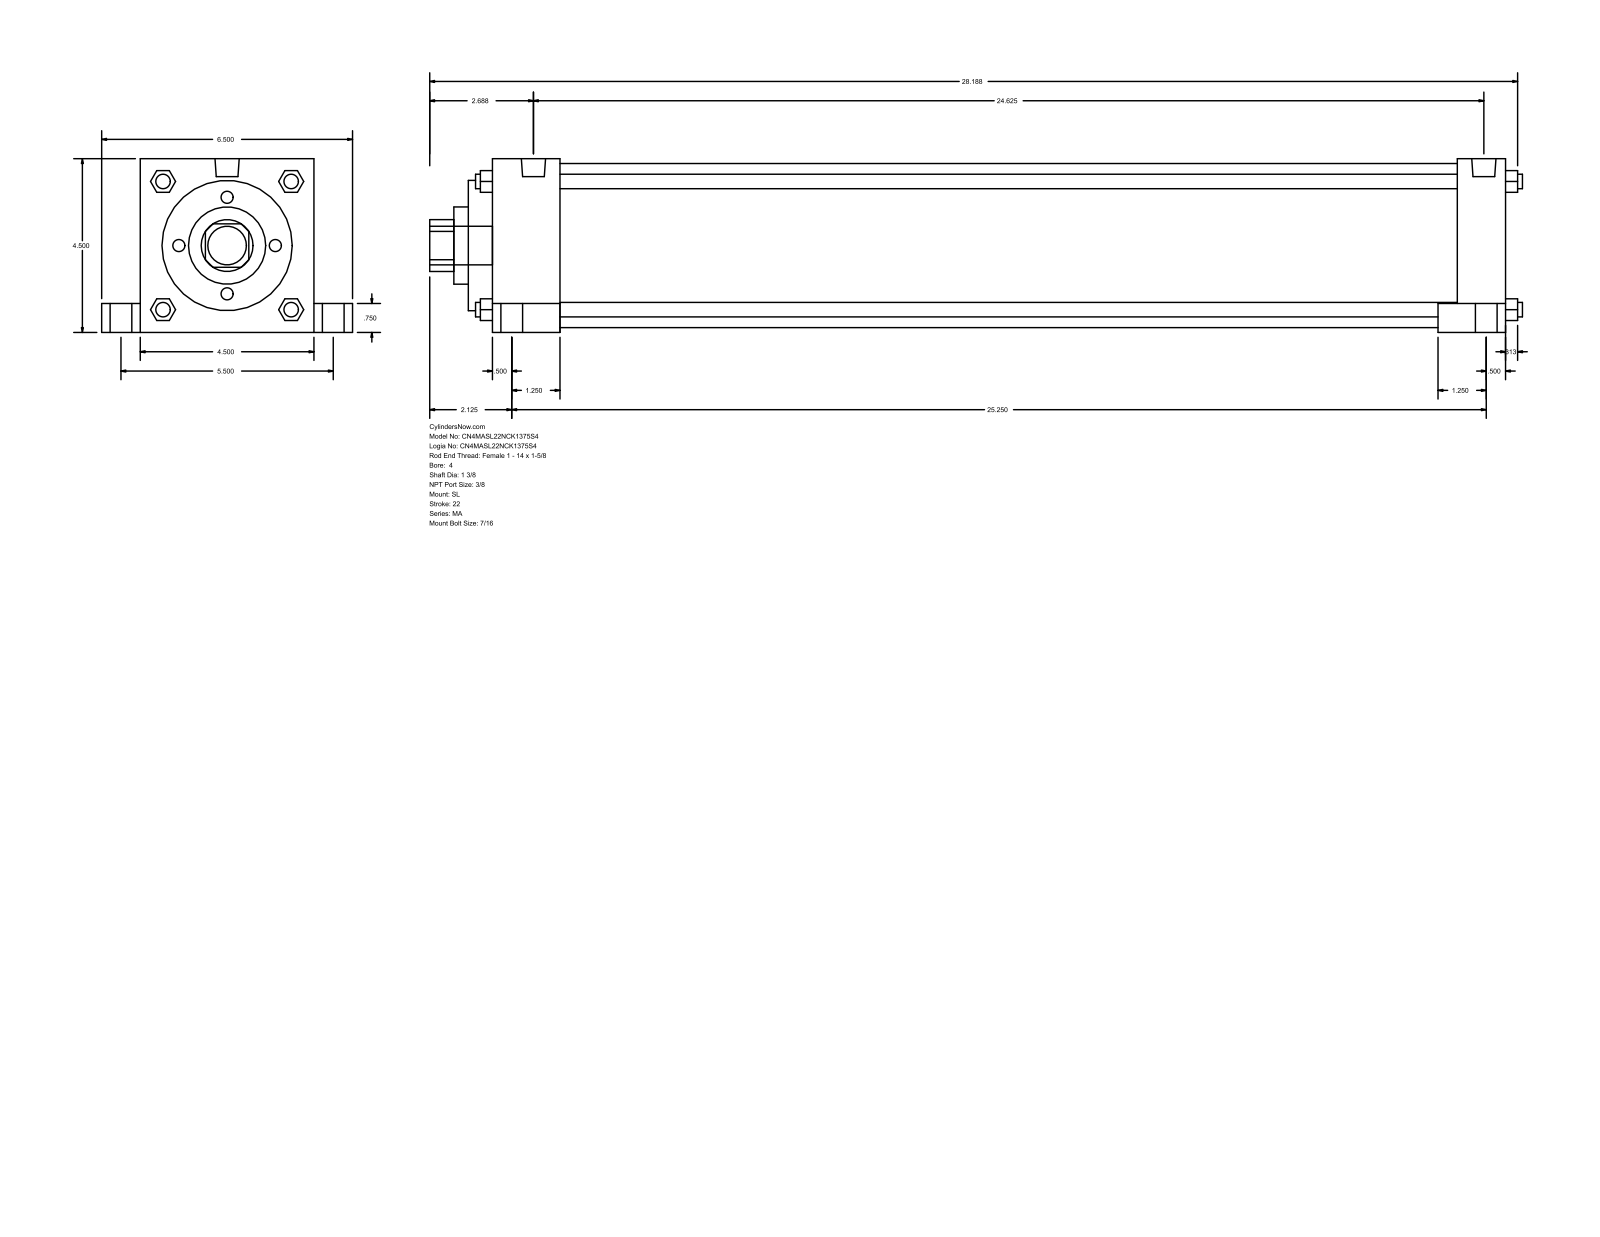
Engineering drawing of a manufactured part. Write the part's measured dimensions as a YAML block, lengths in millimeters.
part_name: "MA_SL__0400_1.375"
step_written_by: "GSSL Pune (CONFIG_CONTROL_DESIGN)"
units: millimeters
bodies: {solids: 0, faces: 150, planar: 113, cylindrical: 37, other: 0}
overall_size: [719.14, 165.1, 114.3]
round_holes:
  - {diameter: 34.92, count: 1}
  - {diameter: 50.8, count: 1}
  - {diameter: 85.72, count: 1}
  - {diameter: 107.95, count: 1}
round_bosses_or_shafts:
  - {diameter: 20.64, count: 4}
  - {diameter: 14.29, count: 4}
  - {diameter: 11.11, count: 4}
  - {diameter: 9.53, count: 4}
  - {diameter: 15.93, count: 2}
  - {diameter: 25.4, count: 1}
partial_cylinders:
  - {radius: 17.06, count: 1}
face_to_face_distances: [114.3, 666.75, 590.55, 682.62, 15.87, 60.32, 44.45, 622.3, 650.87, 635]
